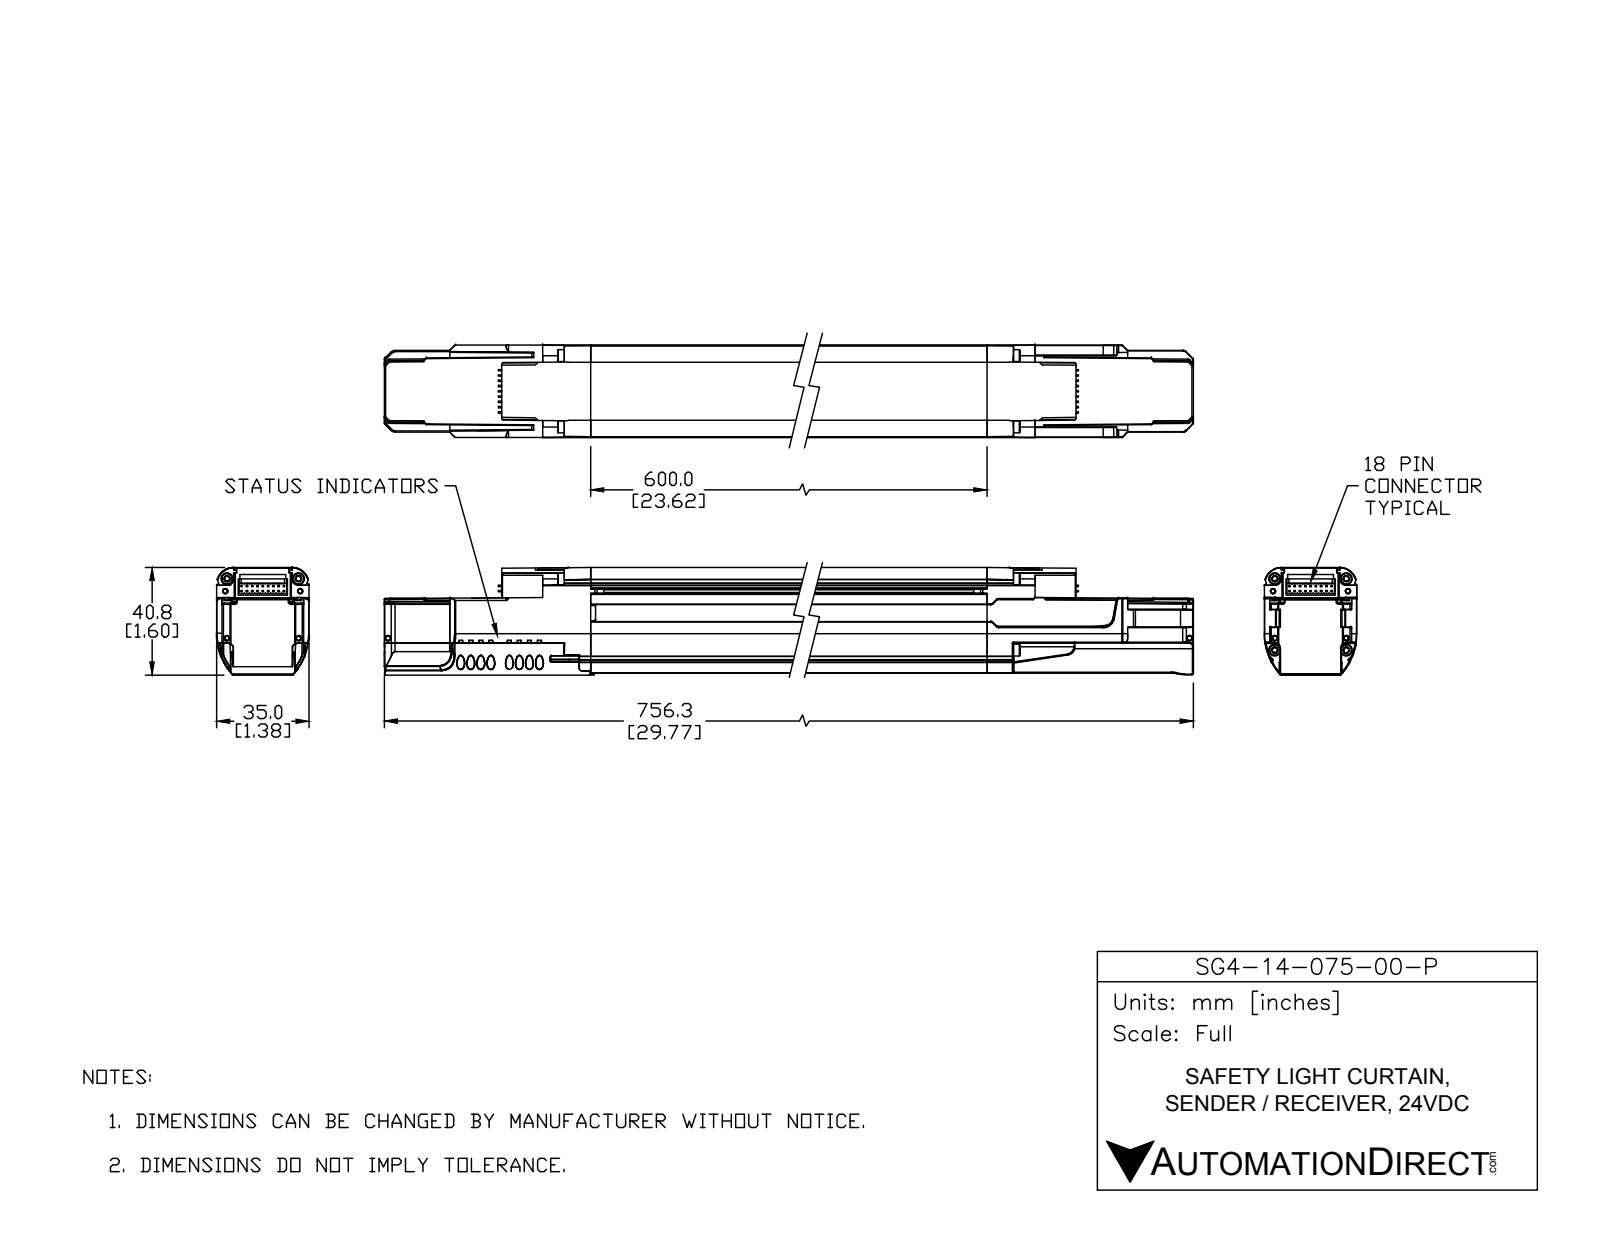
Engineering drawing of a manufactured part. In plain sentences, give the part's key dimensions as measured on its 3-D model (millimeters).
The part is named "SG4-14-075-OO-P". Its 3-D file was written by "SolidWorks 2017 (AUTOMOTIVE_DESIGN)". It is 16 solids with 534 faces: 362 planar, 110 cylindrical and 62 other. Overall it measures 756 by 65.5 by 51.4 millimeters. Its volume is 916 000 cubic millimeters and its surface area 206 800 square millimeters. Round holes: 6 of diameter 1.8, 4 of diameter 2.5, 4 of diameter 4.2, 4 of diameter 5.3, 4 of diameter 6.6, 1 of diameter 1.7, 1 of diameter 1.7. Round bosses or shafts: 4 of diameter 10, 4 of diameter 5. Partial cylindrical surfaces (rounded edges, fillets, slot ends): 16 of radius 2.7, 8 of radius 3, 4 of radius 2.5, 4 of radius 2.8, 2 of radius 2, 2 of radius 3, 2 of radius 3.1, 2 of radius 3.2. The main face-to-face distances are 1.5, 2.1, 0.6, 37.8, 37.2, 39.4, 26.8, 12.2, 25, 25.6. The hole center spacings are 14.5, 559.7, 0.5, 5.2, 5.3, 5.3, 5.8, 18.
